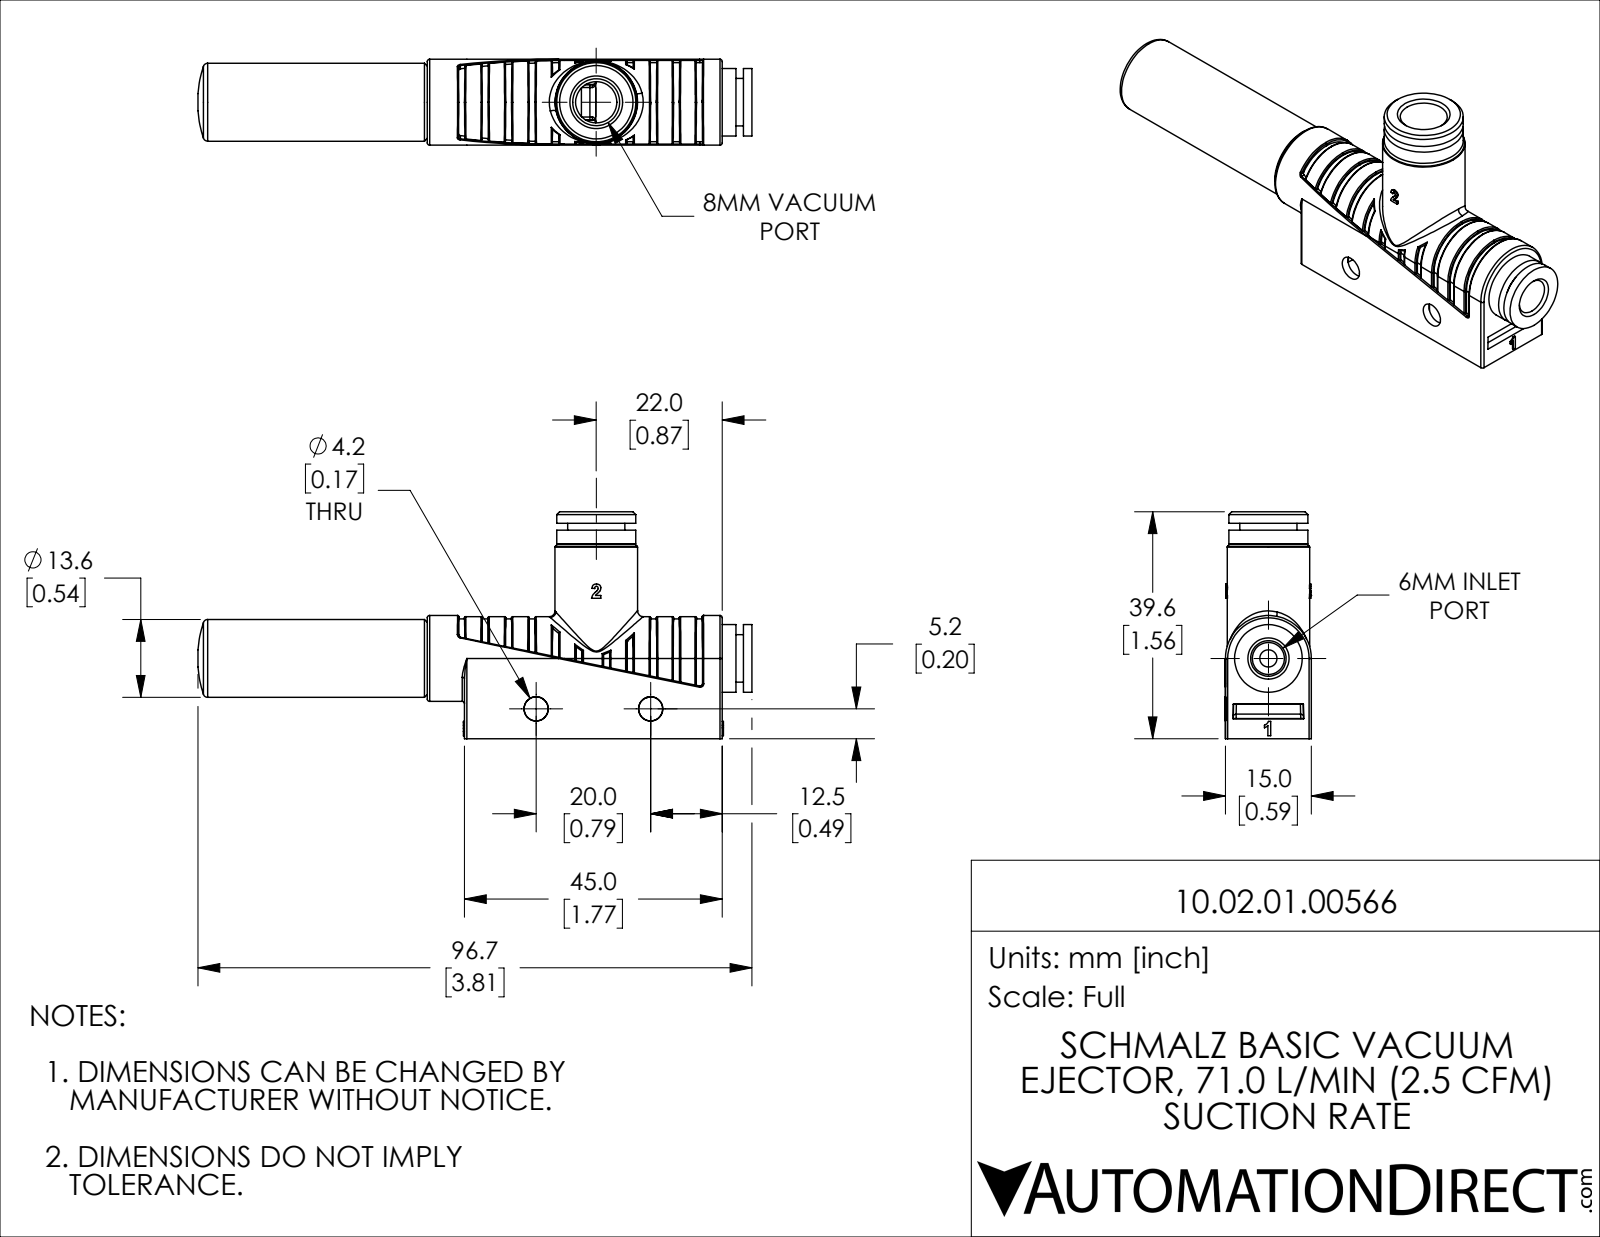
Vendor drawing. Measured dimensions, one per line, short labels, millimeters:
name: 10.02.01.00566
written by: SolidWorks 2021 (CONFIG_CONTROL_DESIGN)
unit: mm
bodies: 5 solids, 517 faces (197 planar, 120 cylindrical, 200 other)
size: 96.74 × 39.6 × 15
volume: 13 850 mm³; area: 12 603 mm²
holes: 1× ⌀3, 1× ⌀6.1, 1× ⌀6.2, 1× ⌀7, 1× ⌀7.6, 1× ⌀8.2, 1× ⌀8.4, 1× ⌀8.57, 1× ⌀9.2, 1× ⌀9.73, 1× ⌀9.9, 1× ⌀11.9
bosses: 1× ⌀15, 1× ⌀14.4, 1× ⌀13.8, 1× ⌀13.6, 1× ⌀11.8, 1× ⌀10, 1× ⌀8.3
rounds: 26× R0.2, 12× R0.4, 2× R0.5, 1× R1, 1× R2.1, 1× R6.2, 1× R6.84, 1× R6.9
face distances: 15, 13.9, 26.1, 5.2, 2.4, 50.2, 20.04, 6.14, 6.06, 19.96
